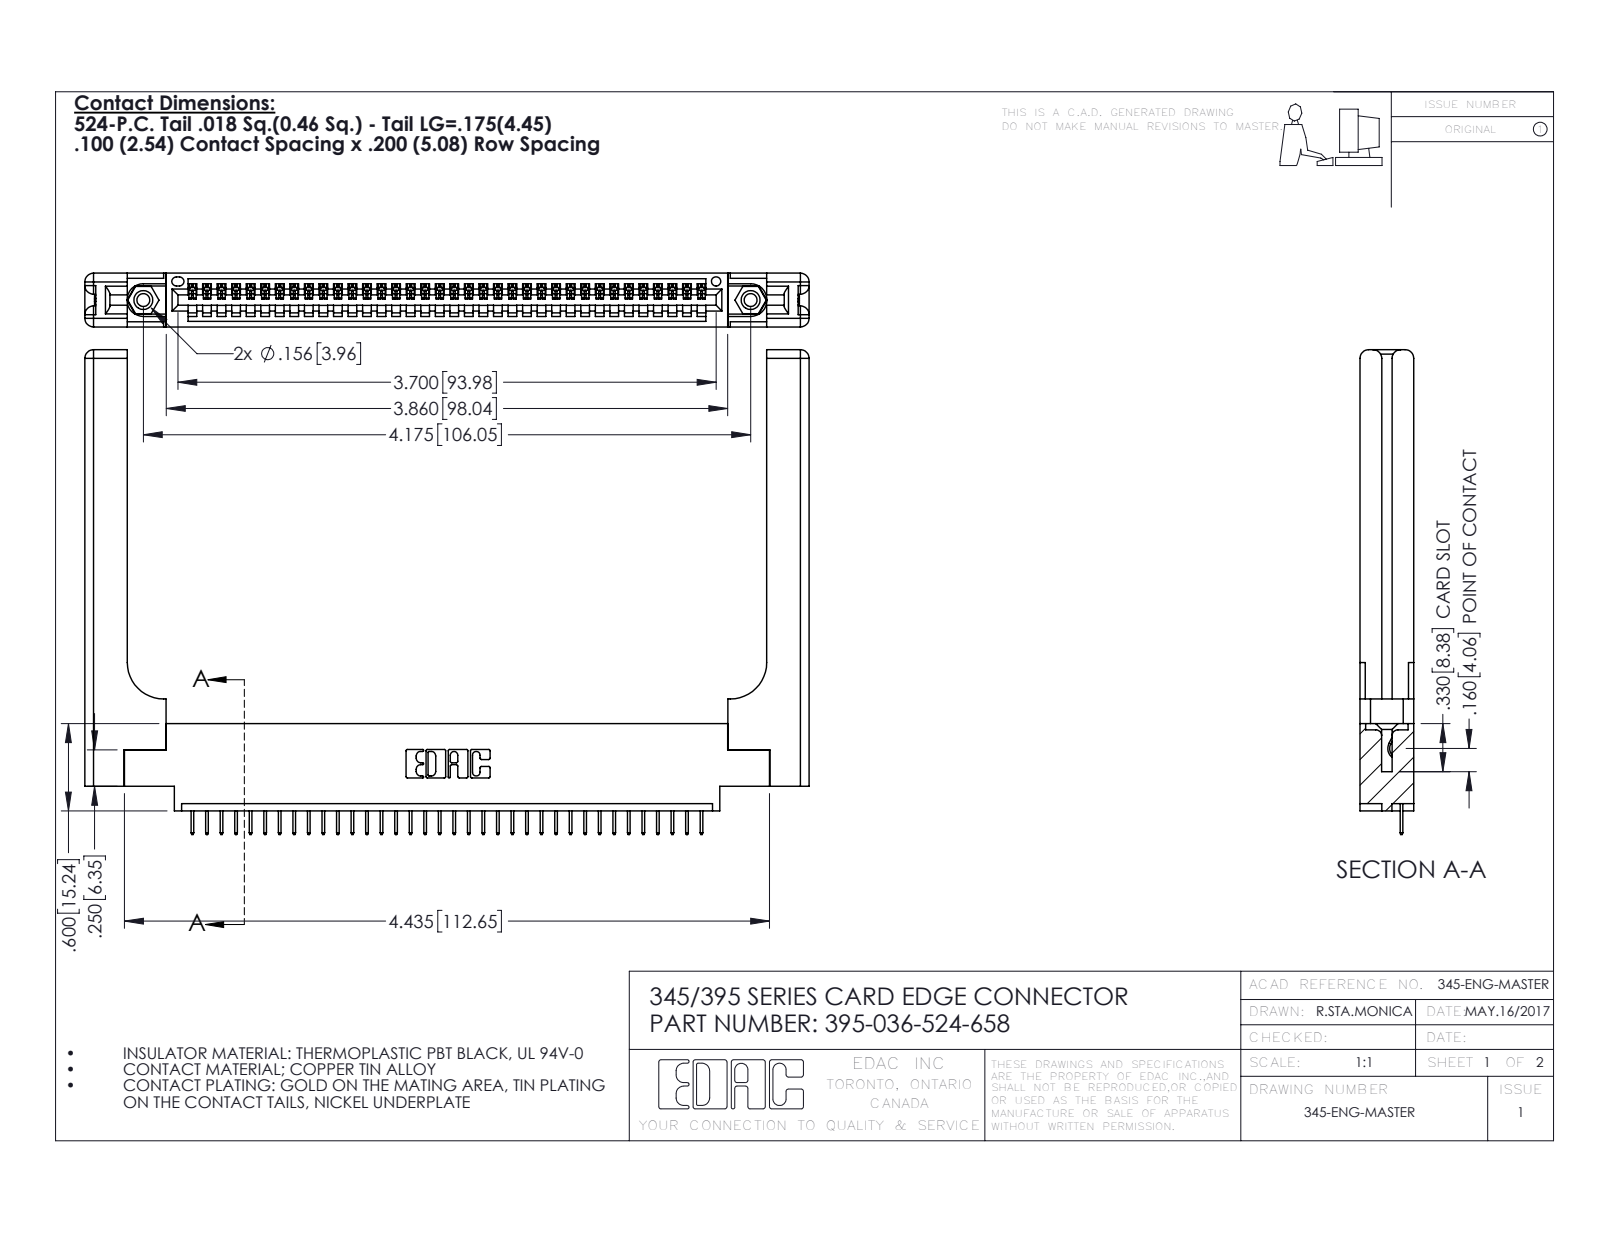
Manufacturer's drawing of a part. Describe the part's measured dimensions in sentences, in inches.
The part is named "345-292-001_345-293-124; 345-250-001_345-250-001-102; 345-220-058_345-220-058; 345 Part_0.170 Offset - 0.156 Dia-TH (+1 more)". Its 3-D file was written by "SolidWorks 2016 (CONFIG_CONTROL_DESIGN)". It is 41 solids with 2618 faces: 1888 planar, 670 cylindrical and 60 other. Overall it measures 4.979 by 3.332 by 0.37 inches. Its volume is 1.233 cubic inches and its surface area 31.7 square inches. Round holes: 2 of diameter 0.089, 2 of diameter 0.125, 2 of diameter 0.156, 1 of diameter 0.064. Round bosses or shafts: 2 of diameter 0.155. Partial cylindrical surfaces (rounded edges, fillets, slot ends): 72 of radius 0.006, 22 of radius 0.01, 16 of radius 0.06, 6 of radius 0.007, 6 of radius 0.031, 3 of radius 0.026, 2 of radius 0.03, 2 of radius 0.031. The main face-to-face distances are 0.37, 0.072, 0.298, 0.098, 0.272, 0.025, 0.2, 0.148, 0.15, 0.225. The hole center spacings are 0.27, 3.939, 4.175.
